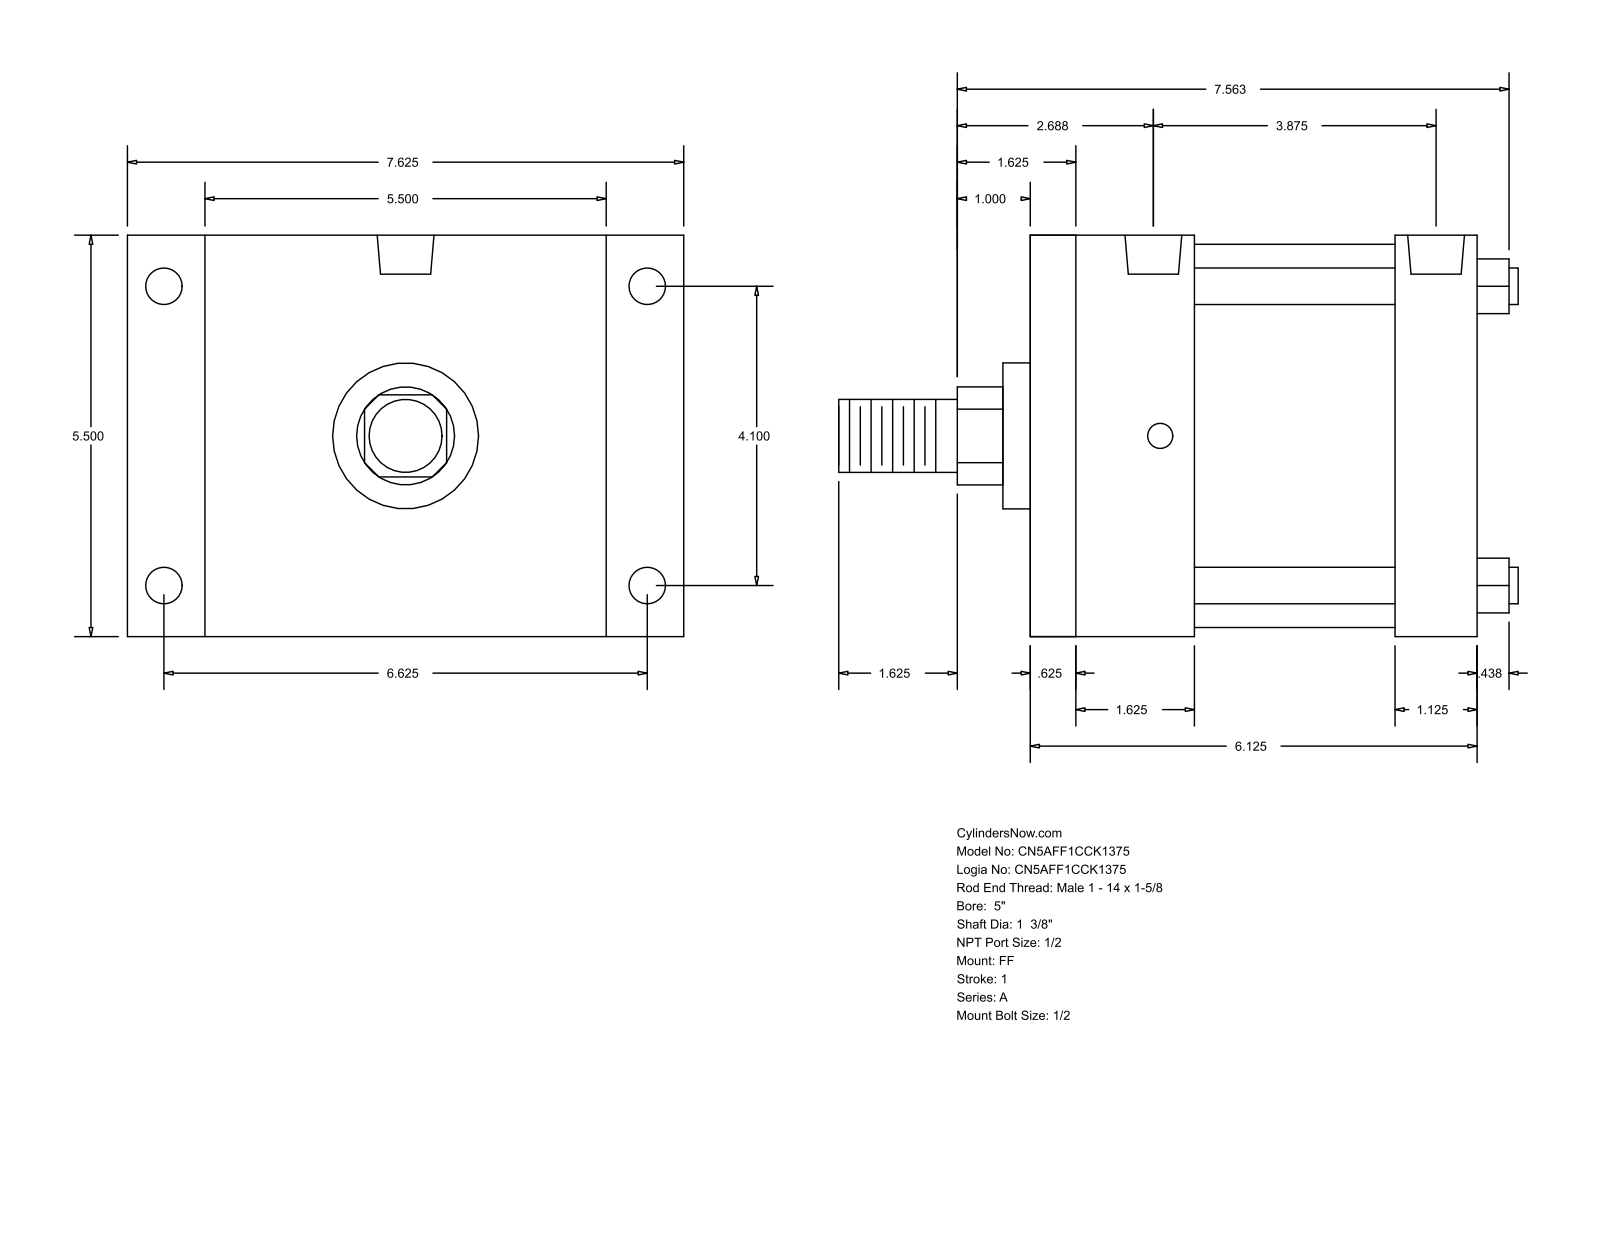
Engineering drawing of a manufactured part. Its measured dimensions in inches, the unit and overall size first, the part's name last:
Units: inches
Overall size (bounding box): 9.313 × 7.625 × 5.5
Round holes (diameter × count): ⌀0.344 ×4, ⌀0.5 ×4, ⌀0.778 ×2
Round bosses / shafts (diameter × count): ⌀0.5 ×4, ⌀5.25 ×1, ⌀2 ×1, ⌀1.375 ×1, ⌀1 ×1
Partial cylindrical surfaces — rounded edges, fillets, slot ends (radius × count): R0.672 ×1
Main face-to-face distances: 5.5, 6.125, 0.625, 2.25, 4.375, 1.125, 2.75, 6.563, 5, 1.625
Hole centre spacings: 0.094, 3.687, 3.781, 4.1, 6.625, 7.791, 3.875
Bodies: 0 solids, 92 faces (64 planar, 28 cylindrical, 0 other)
Part name (STEP PRODUCT): A_FF__0500_1.375
STEP written by: GSSL Pune (CONFIG_CONTROL_DESIGN)
